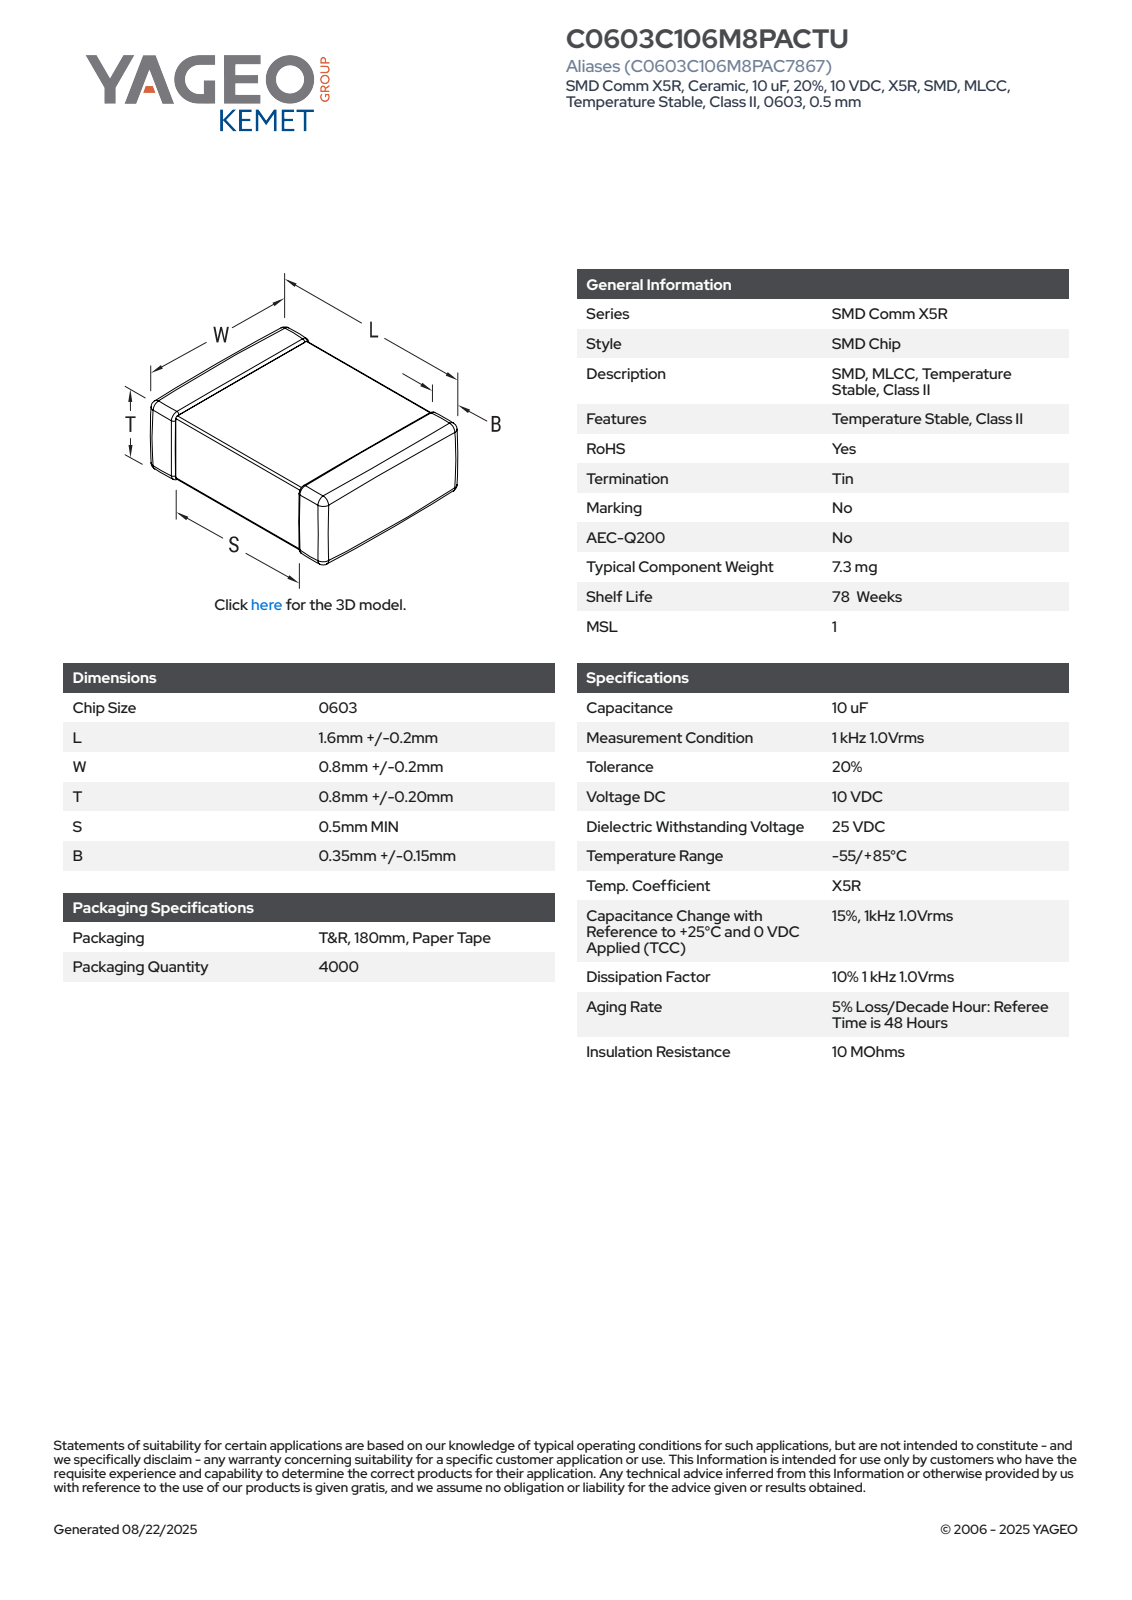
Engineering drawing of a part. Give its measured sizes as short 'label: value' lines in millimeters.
name: CCS_CCSTD_0603_L1.8W1T1B0.35
written by: SolidWorks 2021 (AUTOMOTIVE_DESIGN)
unit: mm
bodies: 4 solids, 125 faces (71 planar, 38 cylindrical, 16 other)
size: 1.8 × 1 × 1
volume: 2 mm³; area: 9 mm²
face distances: 0.98, 1, 0.96, 1.8, 0.82, 0.97, 0.83, 0.4, 0.6, 0.41
